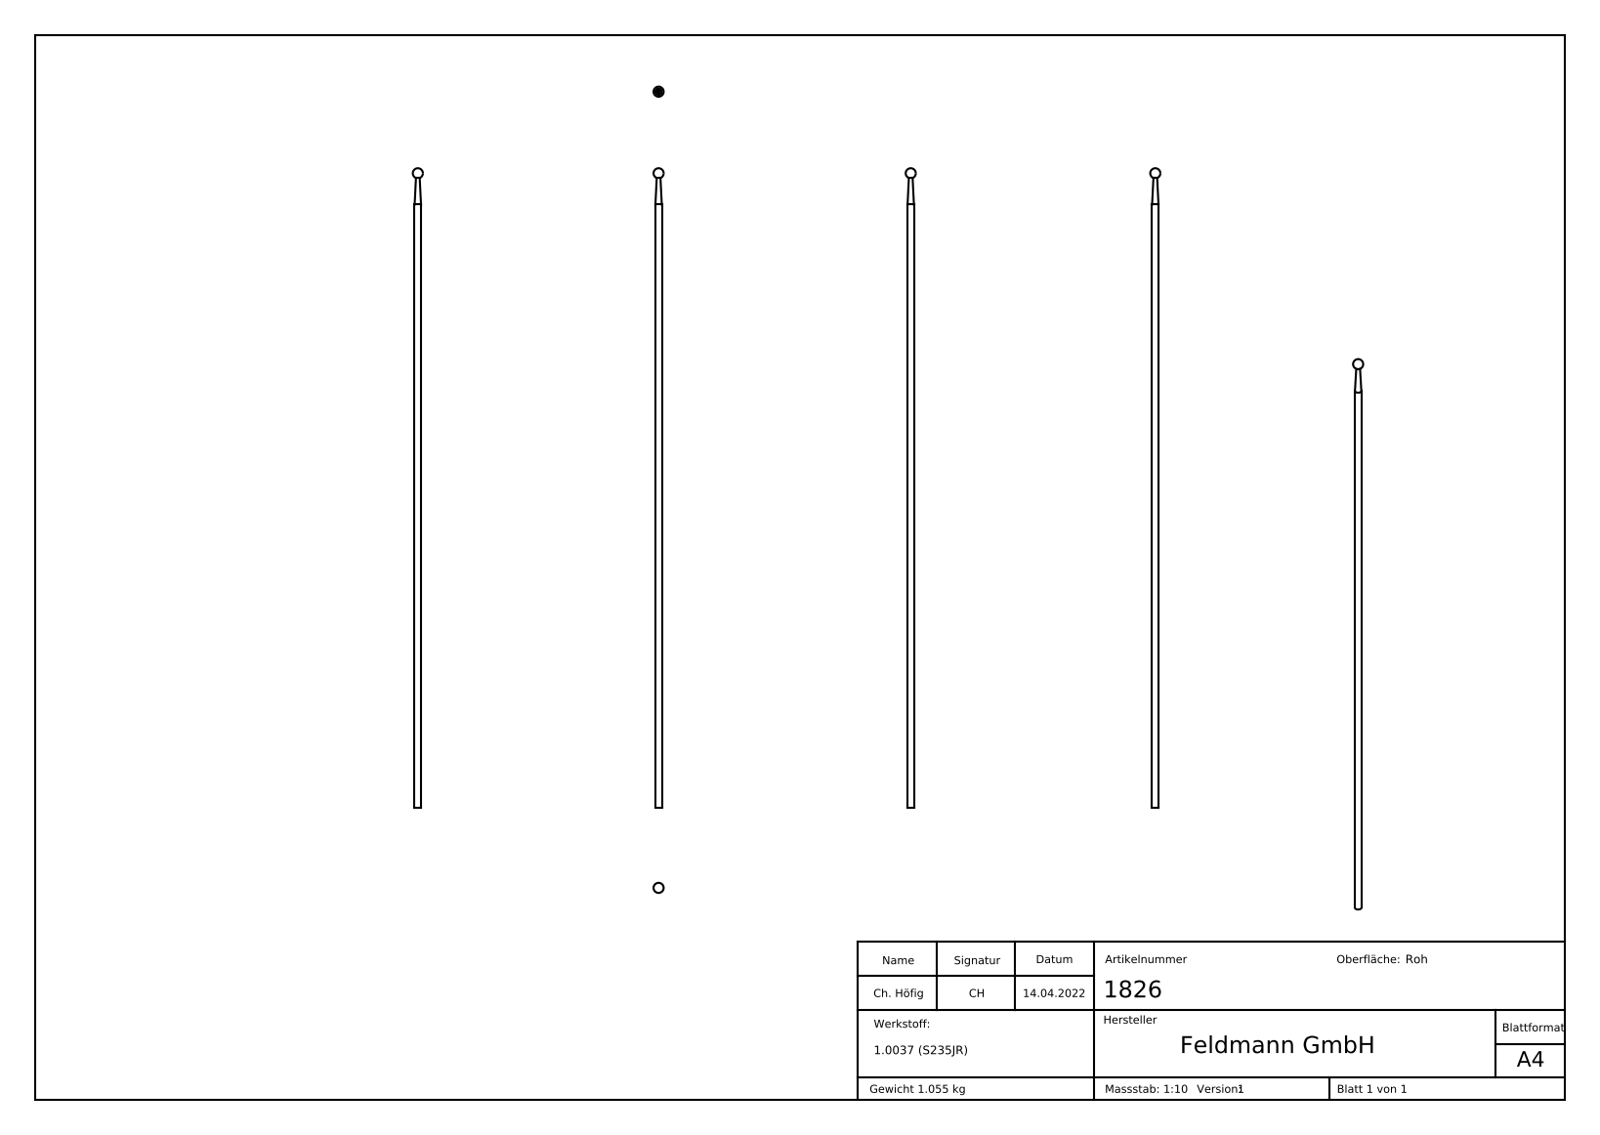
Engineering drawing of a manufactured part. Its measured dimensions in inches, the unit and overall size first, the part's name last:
Units: inches
Overall size (bounding box): 47.244 × 0.748 × 0.748
Round bosses / shafts (diameter × count): ⌀0.472 ×1
Main face-to-face distances: 0.069, 0.091, 0.077, 0.019, 0.019, 0.064, 0.016, 0.07, 0.048, 0.033
Volume: 8.25 in³ · Surface area: 70.33 in²
Bodies: 1 solid, 214 faces (111 planar, 1 cylindrical, 102 other)
Part name (STEP PRODUCT): 1826
STEP written by: SolidWorks 2018 (CONFIG_CONTROL_DESIGN)
